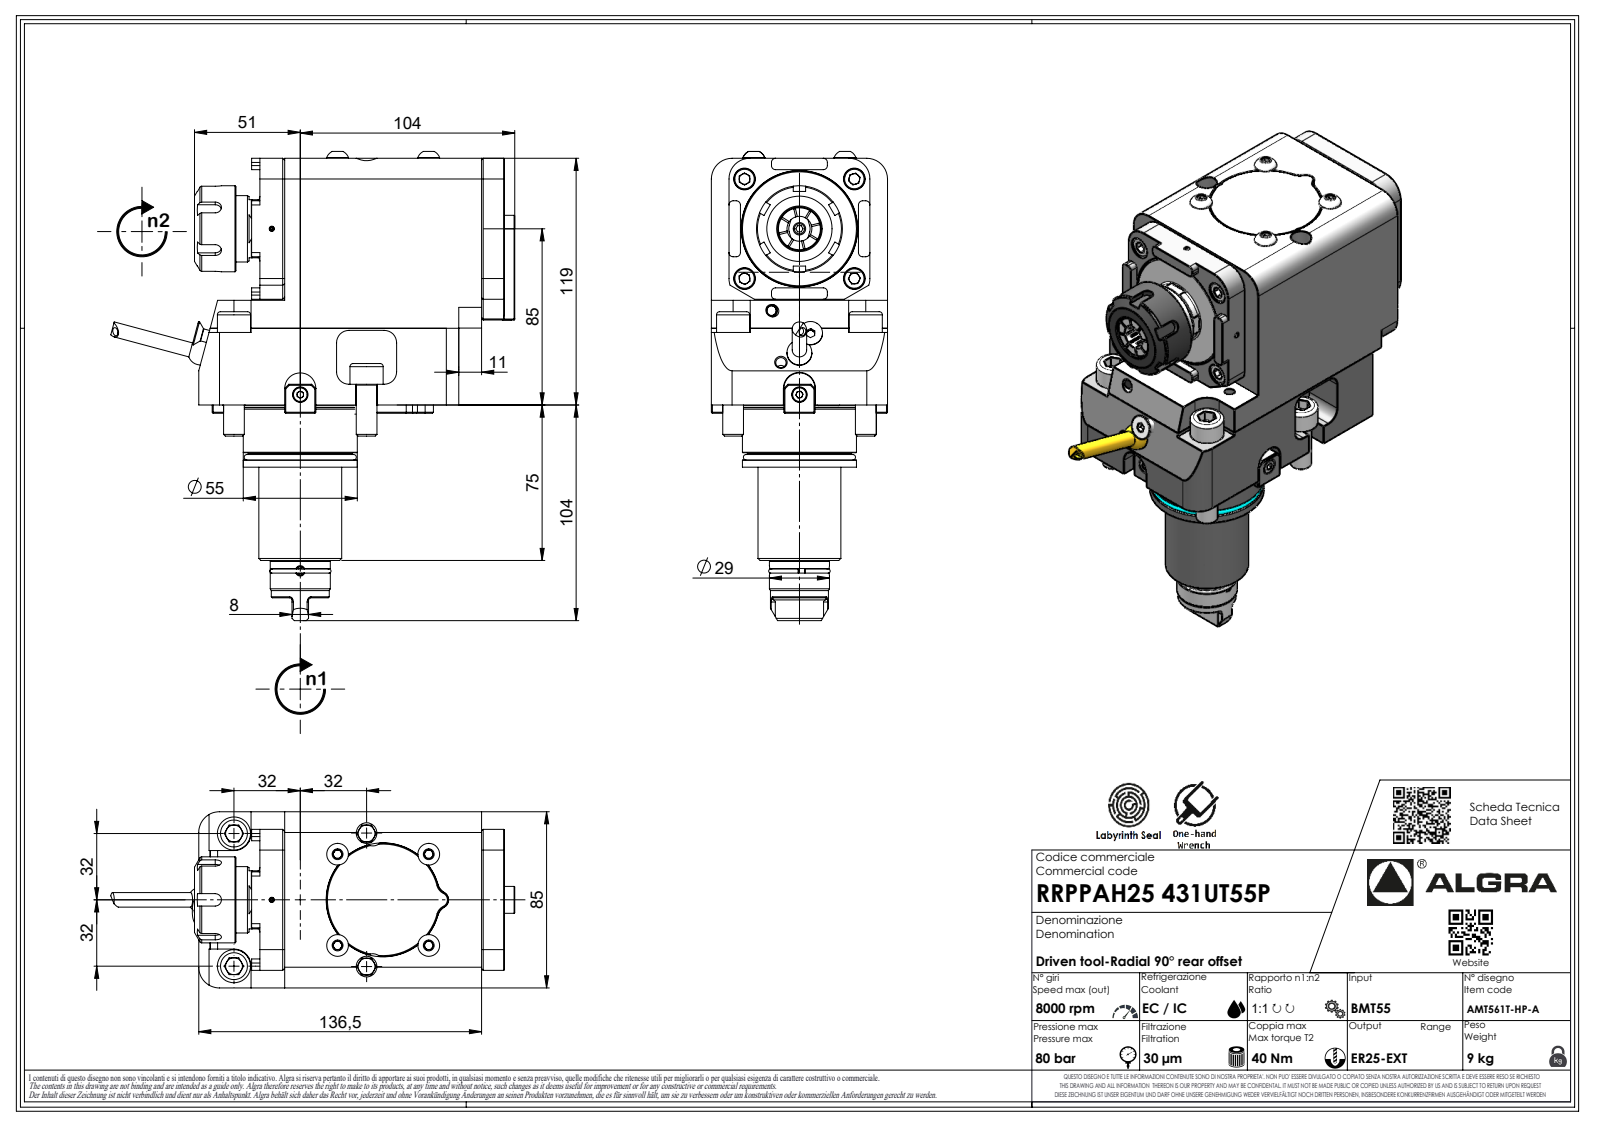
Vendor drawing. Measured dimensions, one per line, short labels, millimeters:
name: RRPPAH25431UT55P
written by: SolidWorks 2023 (AUTOMOTIVE_DESIGN)
unit: mm
bodies: 2 solids, 803 faces (520 planar, 128 cylindrical, 155 other)
size: 226.3 × 194.95 × 85
volume: 1 345 000 mm³; area: 107 091 mm²
holes: 2× ⌀5, 2× ⌀10.5, 1× ⌀2.1, 1× ⌀4, 1× ⌀8.8, 1× ⌀12
bosses: 4× ⌀16, 4× ⌀10.5, 4× ⌀10, 1× ⌀55, 1× ⌀54.6, 1× ⌀50.2, 1× ⌀41.5, 1× ⌀40
rounds: 21× R2, 12× R10, 7× R0.33, 7× R0.52, 7× R3.7, 4× R6, 3× R3, 2× R1
face distances: 85, 119, 11, 118, 22, 96, 50.5, 107, 66, 30
hole spacings: 22.09, 61
